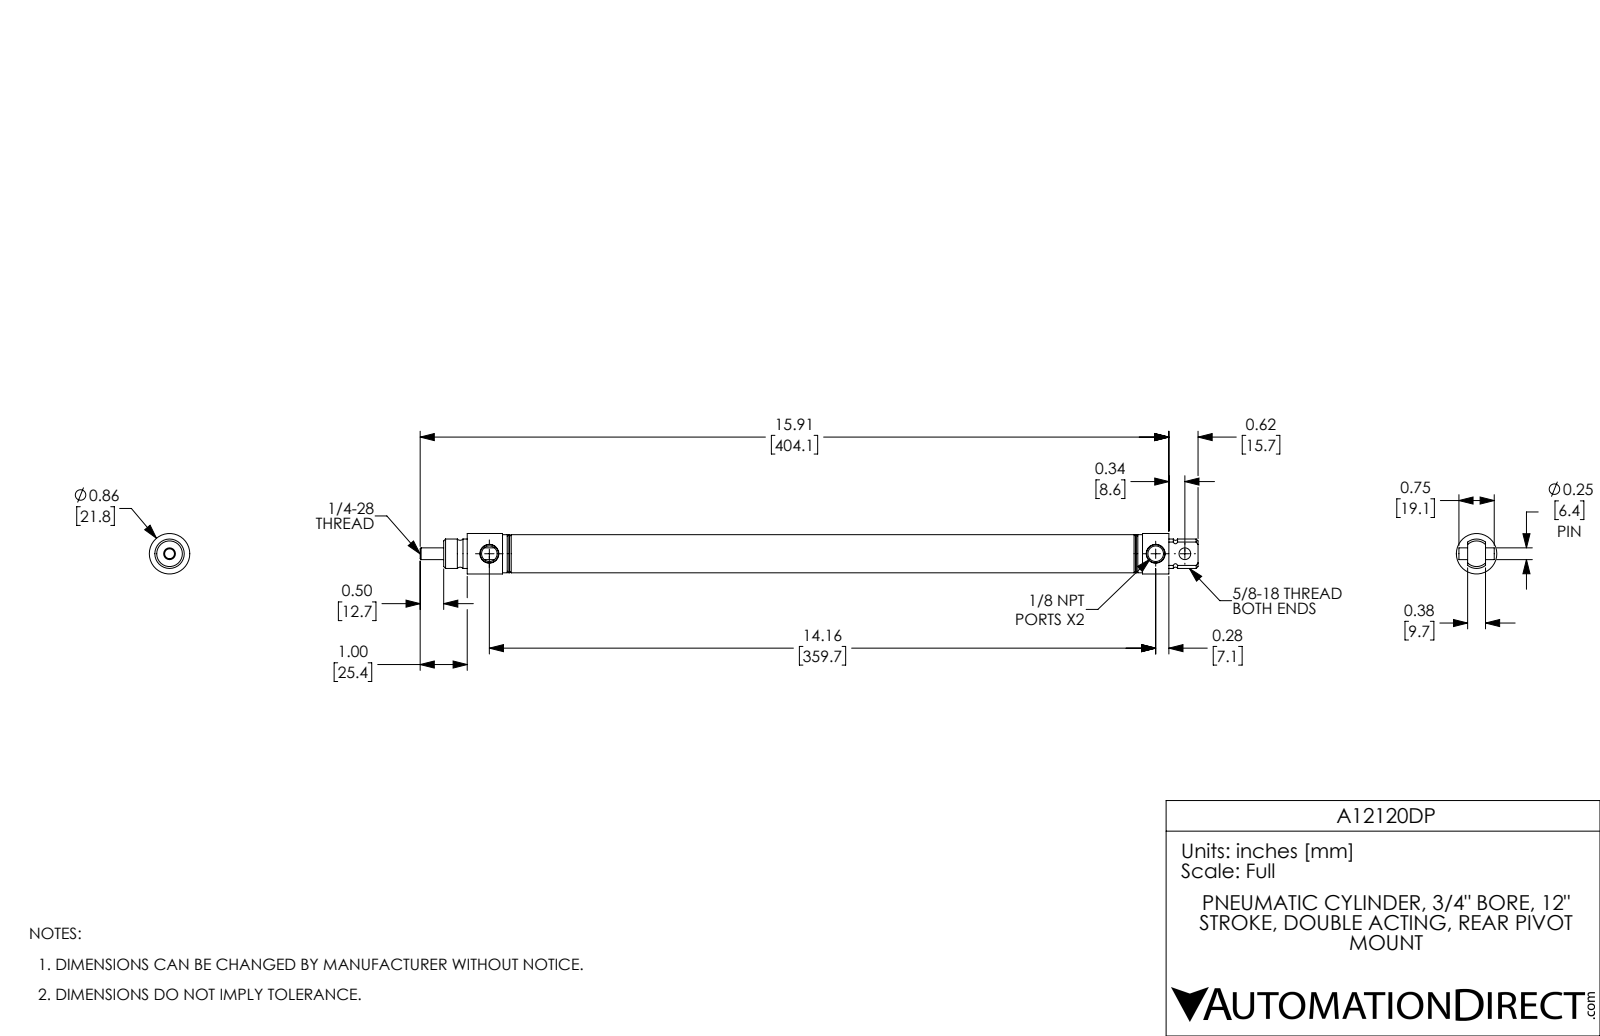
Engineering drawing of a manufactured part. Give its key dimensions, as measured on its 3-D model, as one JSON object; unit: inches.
{"part_name": "A12120DP-MainBody; A12120DP-Rod; A12120DP-PIN; A12120DP", "step_written_by": "SolidWorks 2017 (AUTOMOTIVE_DESIGN)", "units": "inches", "bodies": {"solids": 3, "faces": 91, "planar": 21, "cylindrical": 38, "other": 32}, "overall_size": [16.53, 0.86, 0.86], "volume_in3": 3.287, "surface_area_in2": 88.33, "round_holes": [[0.25, 2], [0.332, 2], [0.75, 1]], "round_bosses_or_shafts": [[0.86, 1], [0.81, 1], [0.625, 1]], "face_to_face_distances": [0.5, 13.705, 12.5, 12, 1.205, 1.705, 13.705, 14.91, 13.205, 1.205], "hole_center_spacings": [0.62, 14.16, 14.78]}
